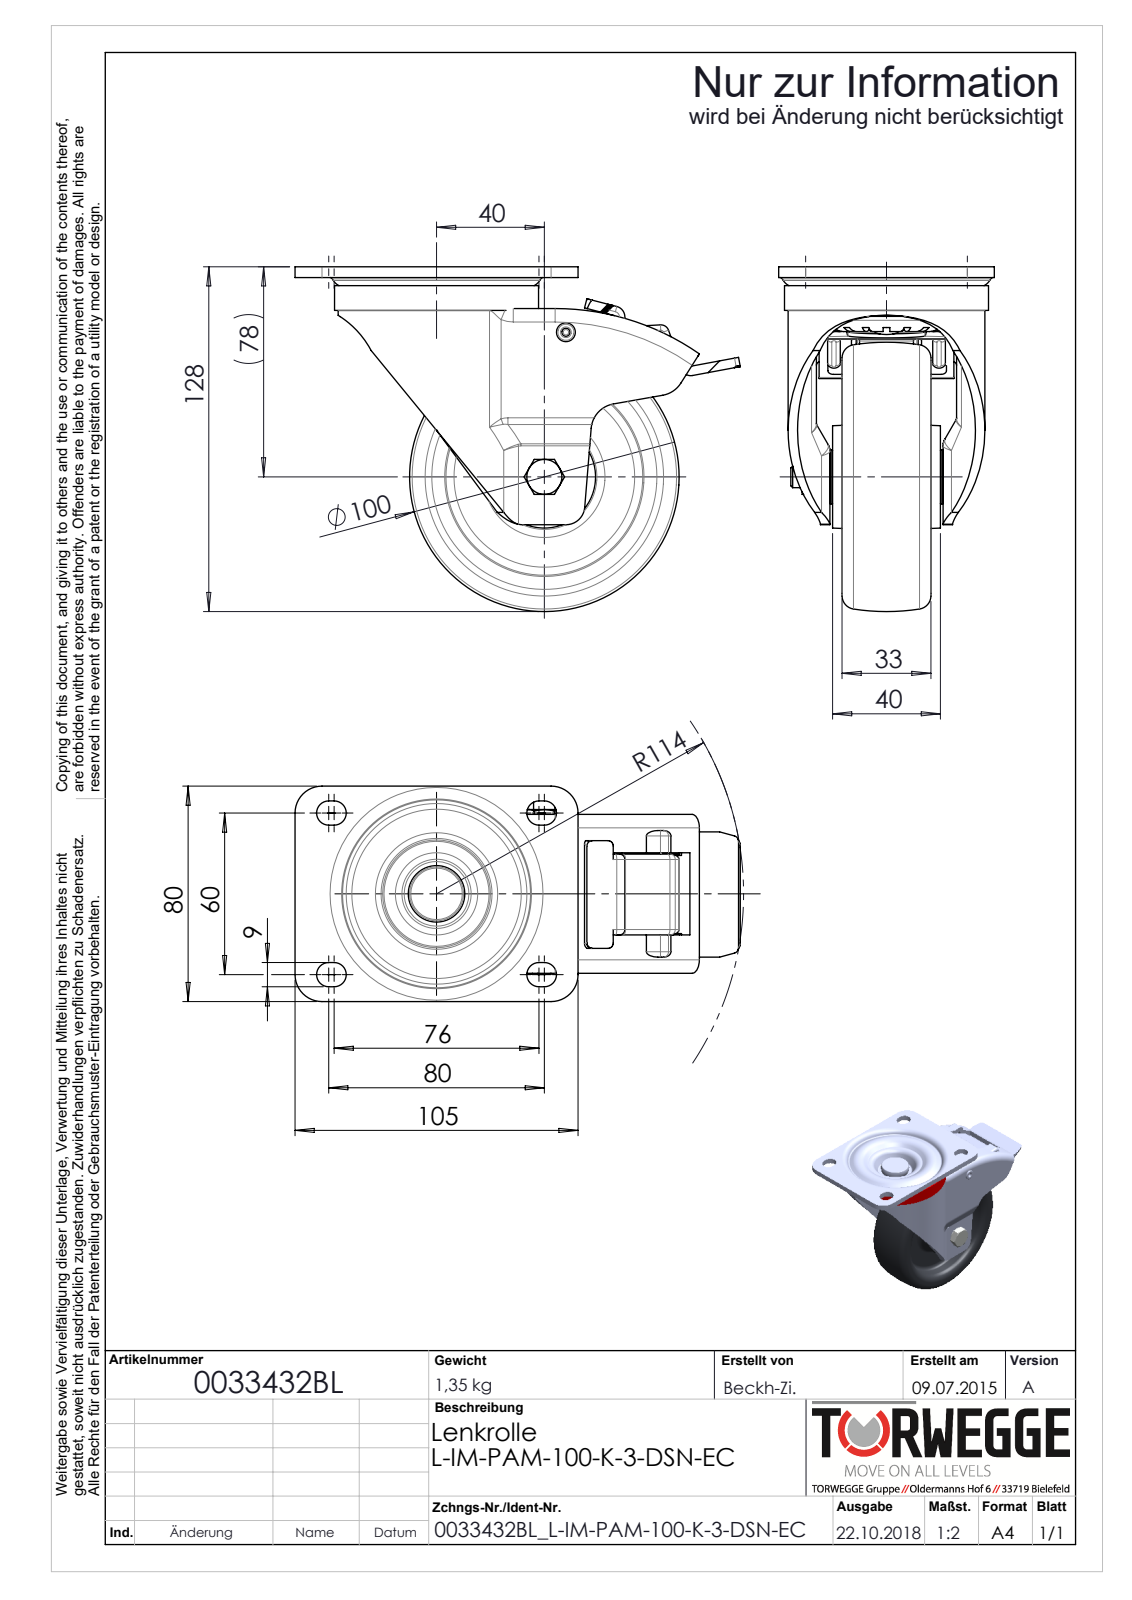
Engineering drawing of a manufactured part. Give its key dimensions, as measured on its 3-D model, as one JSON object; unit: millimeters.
{"part_name": "0033432BL_L-IM-PAM-100-K-3-DSN-EC", "step_written_by": "SolidWorks 2016 (AUTOMOTIVE_DESIGN)", "units": "millimeters", "bodies": {"solids": 22, "faces": 1222, "planar": 589, "cylindrical": 307, "other": 326}, "overall_size": [165.19, 128, 80], "volume_mm3": 327239, "surface_area_mm2": 145493, "round_holes": [[3, 1], [5, 1], [5.2, 1], [6.8, 1], [8, 1], [8.2, 1], [8.5, 1], [12, 1], [12.4, 1], [12.5, 1], [16.8, 1], [23, 1]], "round_bosses_or_shafts": [[75.69, 1], [28, 1], [21, 1], [20, 1], [15, 1], [13, 1], [12.5, 1], [11.9, 1]], "partial_cylinders_radius": [[2, 26], [0.5, 12], [1.5, 12], [4.5, 9], [0.27, 8], [10, 8], [0.15, 7], [0.45, 7]], "face_to_face_distances": [3.5, 1.5, 4, 55.5, 24.5, 34.5, 21, 31, 5, 50.5], "hole_center_spacings": [54.29]}
